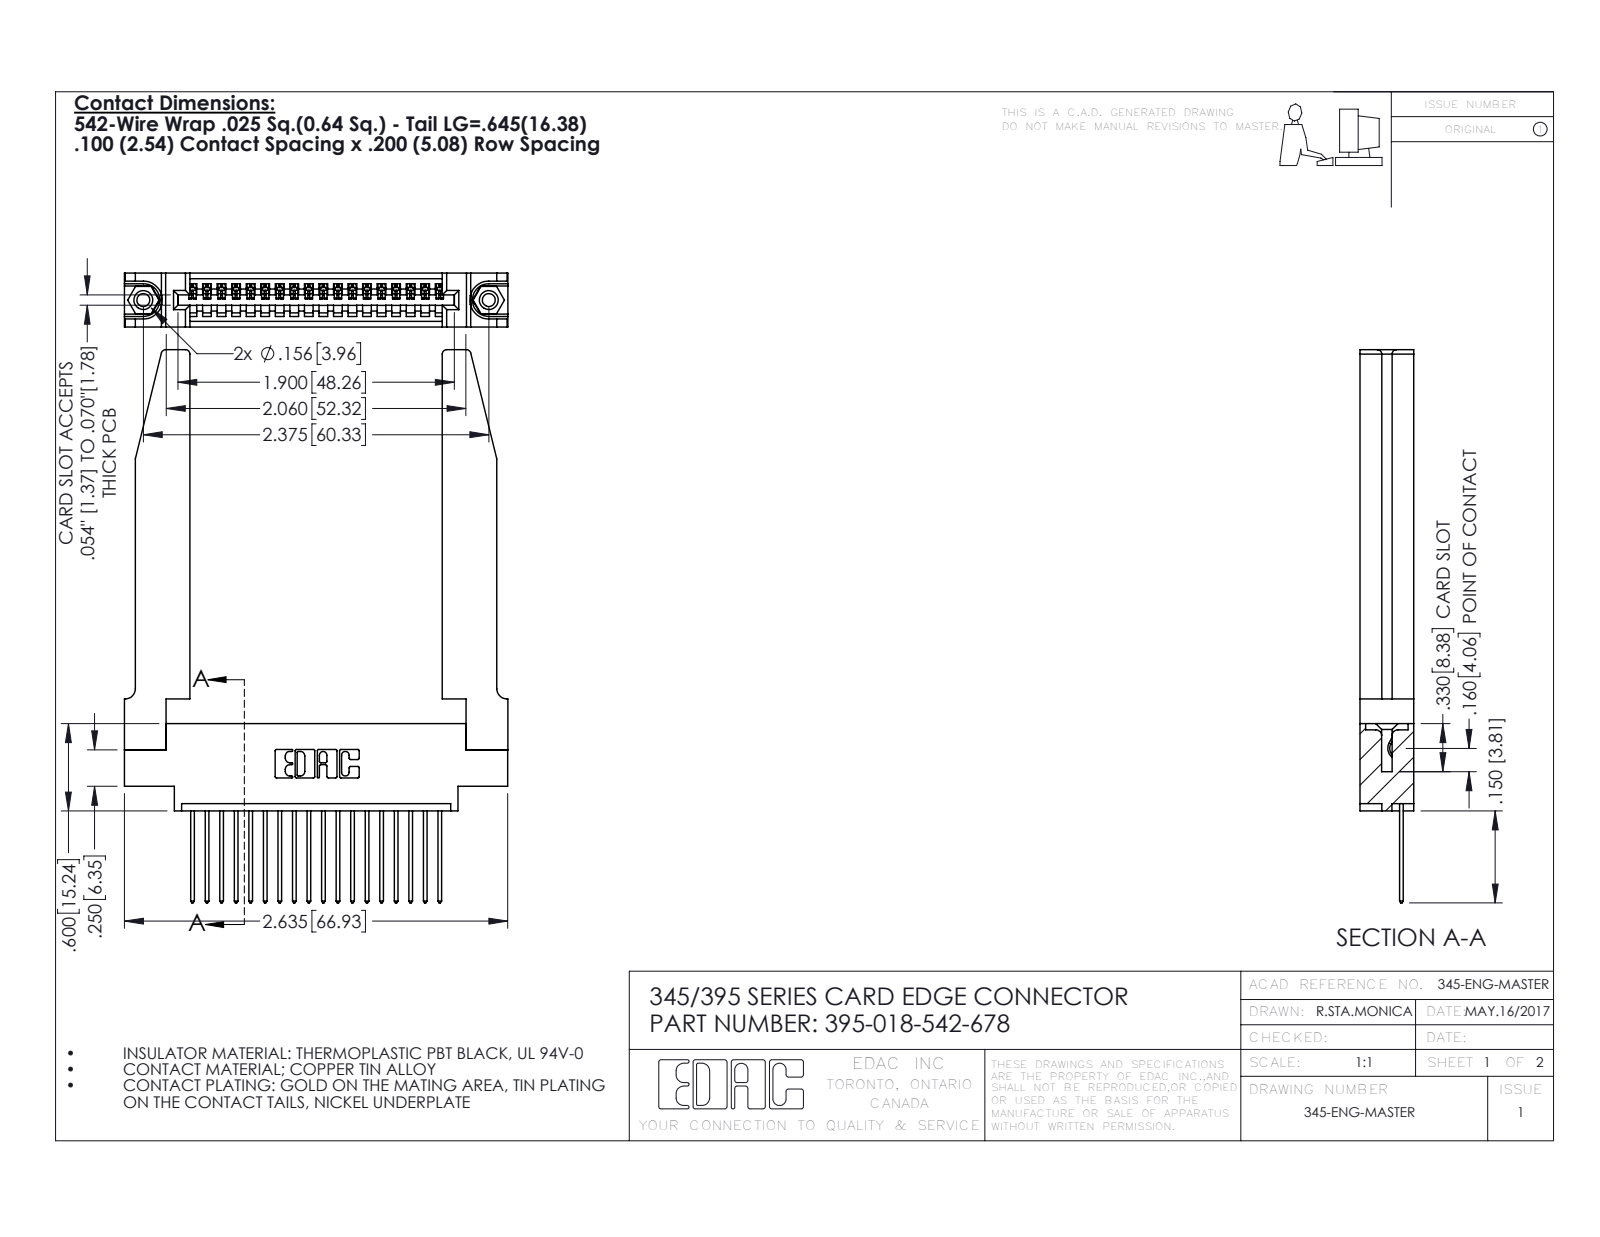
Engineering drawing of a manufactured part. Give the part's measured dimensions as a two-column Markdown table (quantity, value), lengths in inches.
| quantity | value |
| --- | --- |
| part name | 345-220-078_345-220-078; 345-292-001_345-293-142; 345 Part_0.170 Offset - 0.156 Dia-TH; 395-018-542-678 (+1 more) |
| STEP written by | SolidWorks 2016 (CONFIG_CONTROL_DESIGN) |
| units | inches |
| bodies | 23 solids, 1408 faces (946 planar, 410 cylindrical, 52 other) |
| overall size | 3.802 × 2.636 × 0.37 |
| volume | 0.846 in³ |
| surface area | 23.24 in² |
| round holes (diameter × count) | 0.089 × 2, 0.125 × 2, 0.156 × 2, 0.064 × 1 |
| round bosses / shafts (diameter × count) | 0.155 × 2 |
| partial cylindrical surfaces (radius × count) | 0.006 × 36, 0.01 × 36, 0.01 × 22, 0.03 × 8, 0.007 × 6, 0.031 × 6, 0.026 × 3, 0.031 × 2 |
| main face-to-face distances | 0.37, 0.072, 0.298, 0.098, 0.272, 0.025, 0.15, 0.148, 0.2, 0.22 |
| hole center spacings | 0.27, 2.141, 2.375 |
